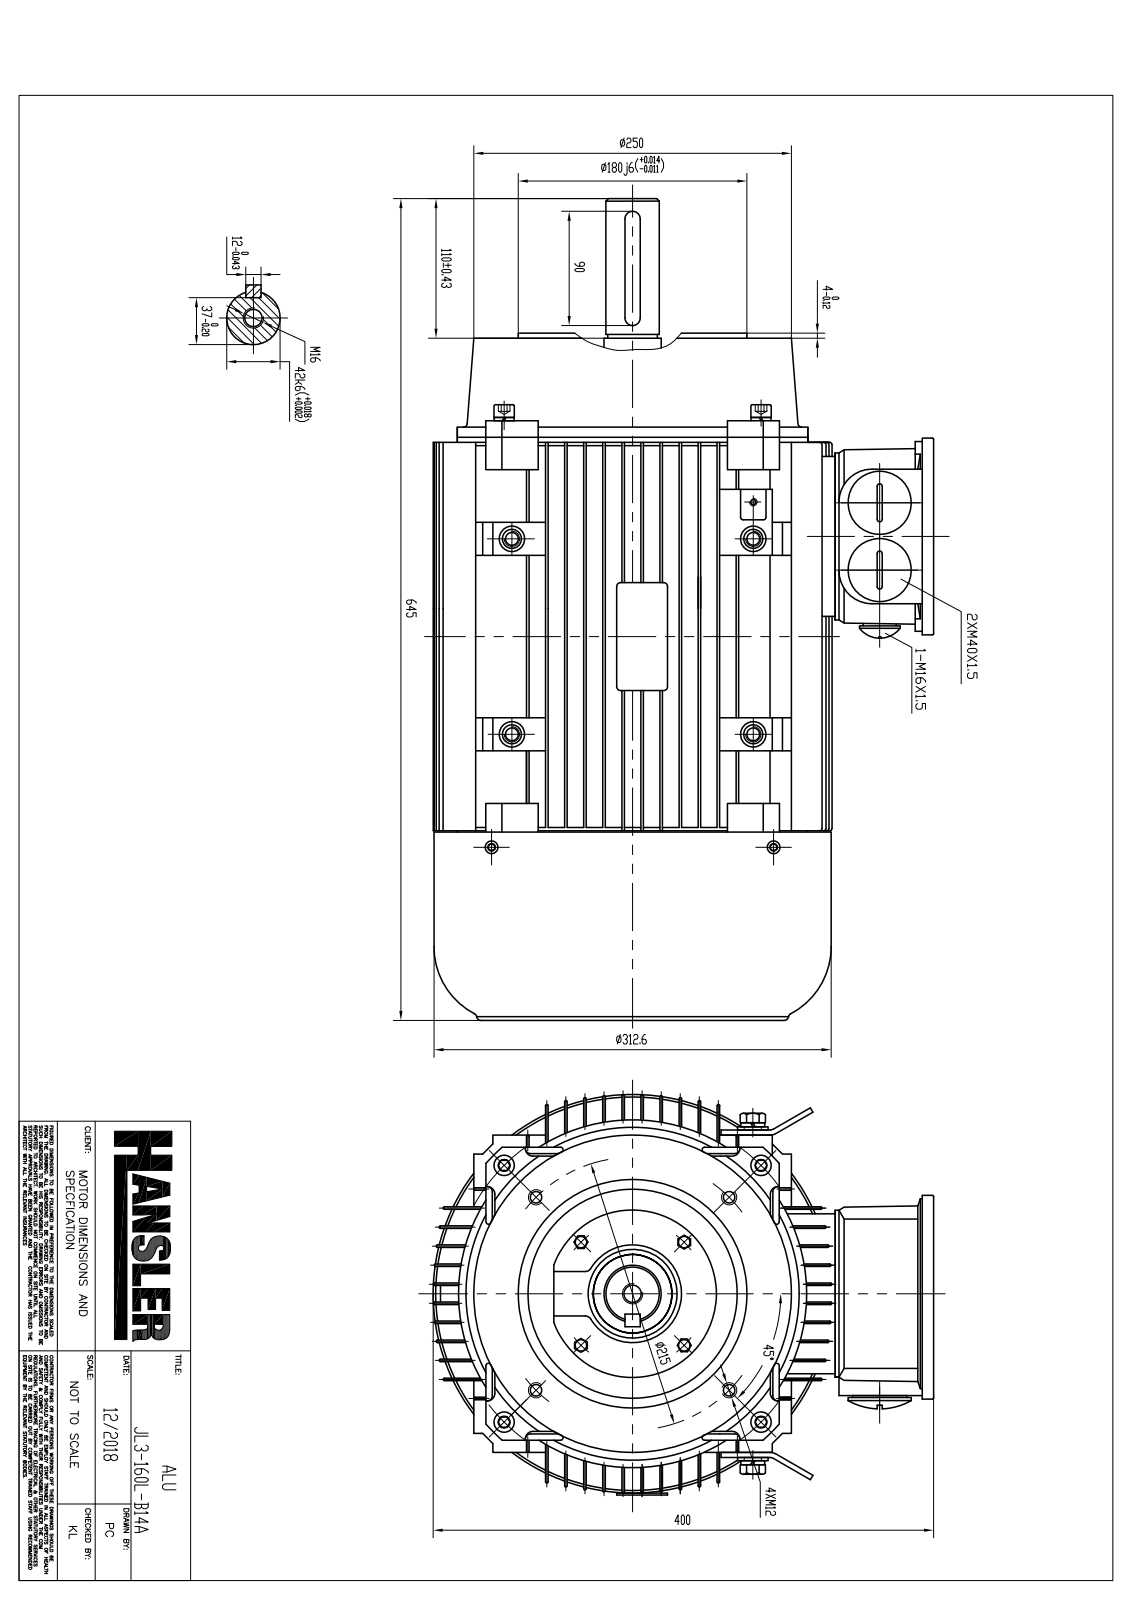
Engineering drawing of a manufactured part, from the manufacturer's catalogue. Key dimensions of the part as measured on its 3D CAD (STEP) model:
Part name (STEP PRODUCT): JL3-160L-B14A
STEP written by: SIEMENS PLM Software NX 10.0 (AUTOMOTIVE_DESIGN)
Units: millimetres
Bodies: 61 solids, 8129 faces (3764 planar, 1971 cylindrical, 2394 other)
Overall size (bounding box): 633 × 399.7 × 316
Volume: 7 487 000 mm³ · Surface area: 2 624 000 mm²
Round holes (diameter × count): ⌀5 ×28, ⌀4.12 ×12, ⌀10 ×12, ⌀8 ×9, ⌀8.39 ×8, ⌀9.1 ×8, ⌀21 ×8, ⌀5.25 ×5, ⌀5.3 ×5, ⌀6 ×5, ⌀4.2 ×4, ⌀5.48 ×4
Round bosses / shafts (diameter × count): ⌀8 ×10, ⌀5.38 ×9, ⌀15 ×8, ⌀12.59 ×8, ⌀7.19 ×8, ⌀6 ×8, ⌀10 ×5, ⌀7.85 ×5
Partial cylindrical surfaces — rounded edges, fillets, slot ends (radius × count): R1.2 ×262, R1 ×167, R2 ×74, R3 ×54, R4 ×40, R1.37 ×37, R3.42 ×25, R0.81 ×18
Main face-to-face distances: 15, 30, 45, 2, 60, 75, 13, 17, 90, 28
Hole centre spacings: 202.36, 178.9, 202.24, 154.13, 202.23, 121.91, 202.22, 14.64
